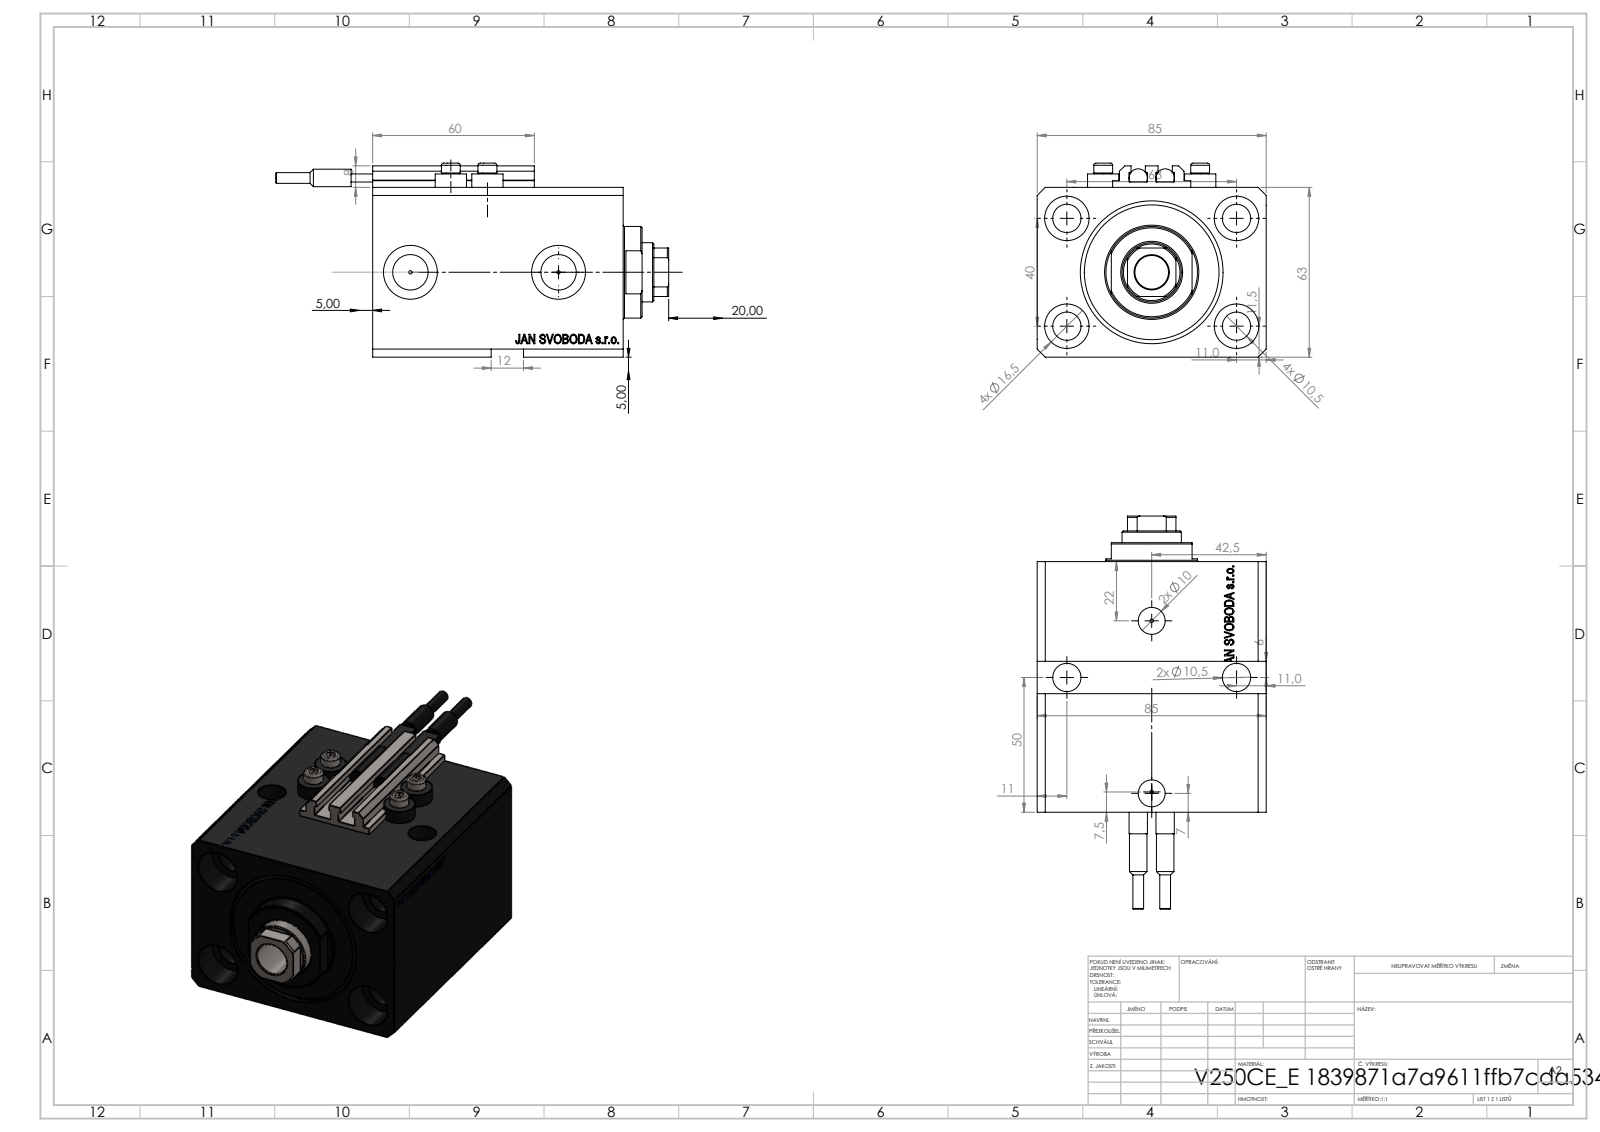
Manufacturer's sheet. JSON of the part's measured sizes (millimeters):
{"part_name": "ALLEN BOLT V250CE; SWITCH_V250CE; V250CE_E_Body; V250CE_C_VCP (+1 more)", "step_written_by": "SolidWorks 2019 (CONFIG_CONTROL_DESIGN)", "units": "millimeters", "bodies": {"solids": 10, "faces": 1139, "planar": 567, "cylindrical": 138, "other": 434}, "overall_size": [146, 85, 72], "volume_mm3": 440825, "surface_area_mm2": 98537, "round_holes": [[10.5, 6], [1.25, 4], [4, 4], [16.5, 4], [10, 2], [13.16, 2], [20, 2], [12.5, 1], [22, 1], [40, 1], [53, 1]], "round_bosses_or_shafts": [[11.6, 4], [7, 4], [6.8, 2], [6.5, 2], [4, 2], [34, 1]], "partial_cylinders_radius": [[0.2, 10], [10.5, 1]], "face_to_face_distances": [63, 85, 93, 17, 76, 11.4, 64.6, 81.6, 3, 65], "hole_center_spacings": [37.31, 63, 13.6, 15.4, 24.96, 28.02, 28.43, 33.62]}
